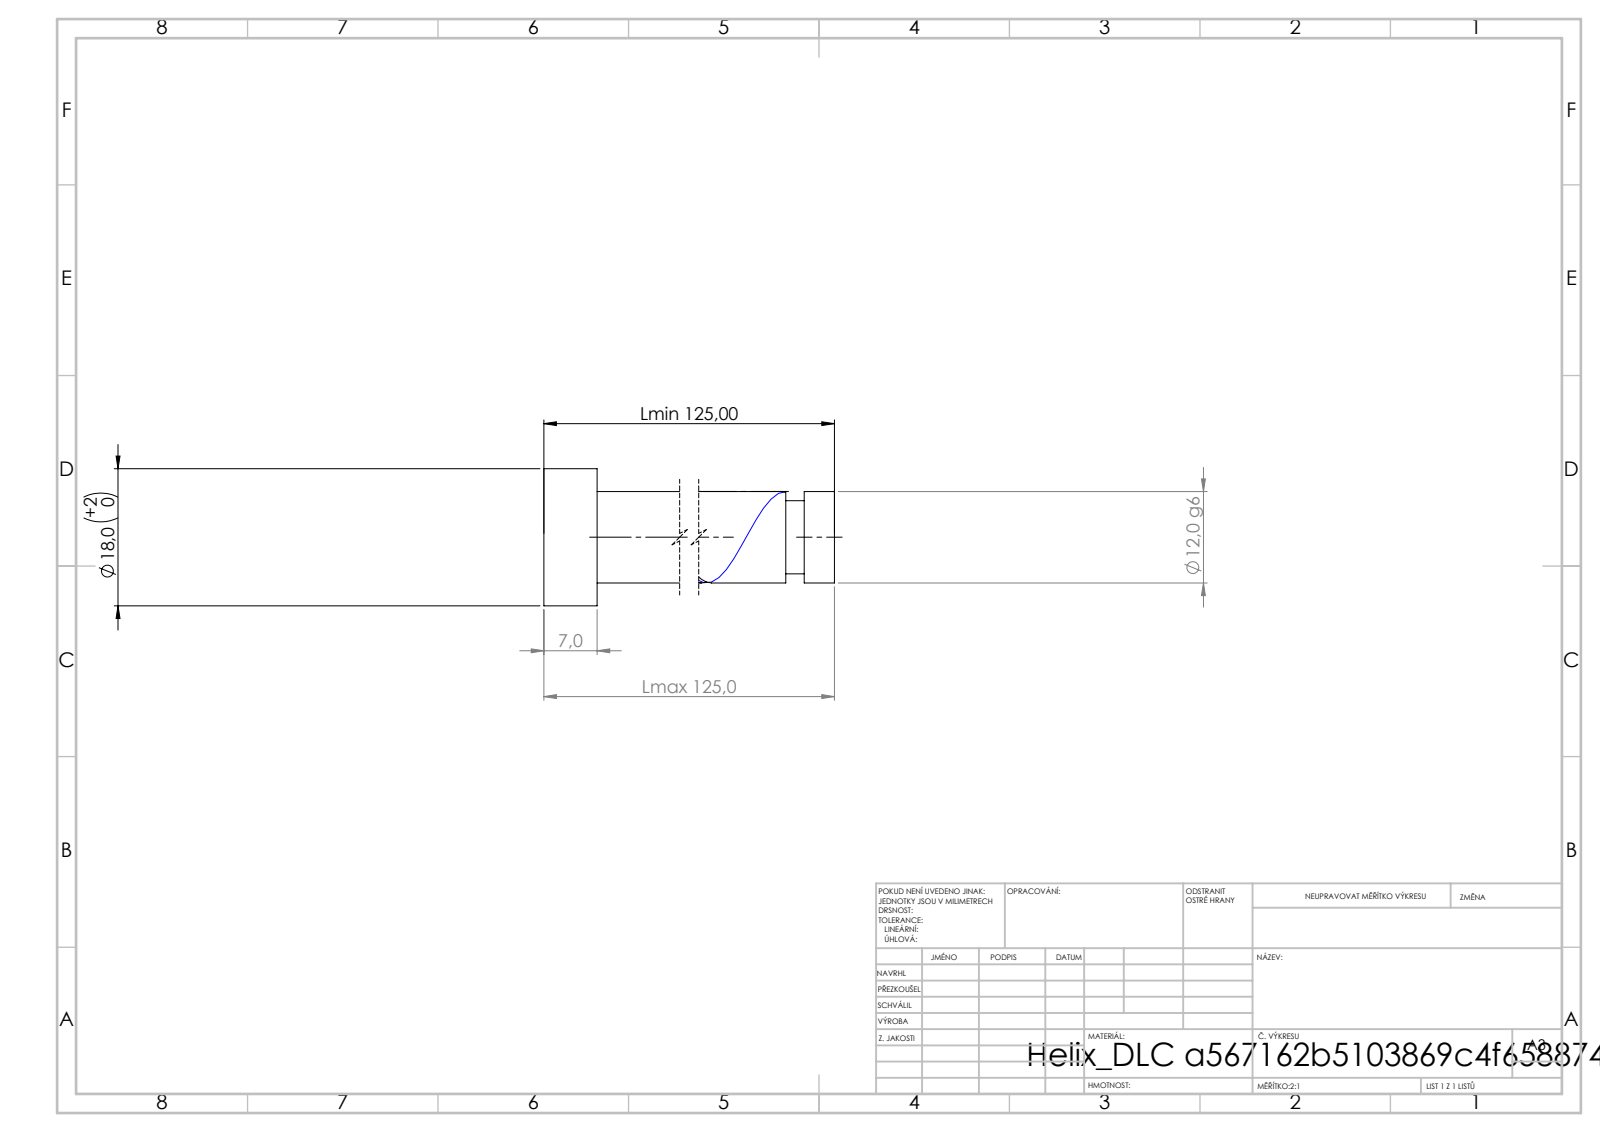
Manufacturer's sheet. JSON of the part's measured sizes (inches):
{"step_written_by": "SolidWorks 2019 (CONFIG_CONTROL_DESIGN)", "units": "inches", "bodies": {"solids": 1, "faces": 21, "planar": 6, "cylindrical": 14, "other": 1}, "overall_size": [4.921, 0.709, 0.709], "volume_in3": 0.909, "surface_area_in2": 8.692, "round_bosses_or_shafts": [[0.709, 1], [0.472, 1], [0.378, 1]], "face_to_face_distances": [0.276, 4.921, 4.646, 4.765, 4.489, 0.157, 4.67, 4.394, 0.094, 0.251]}
